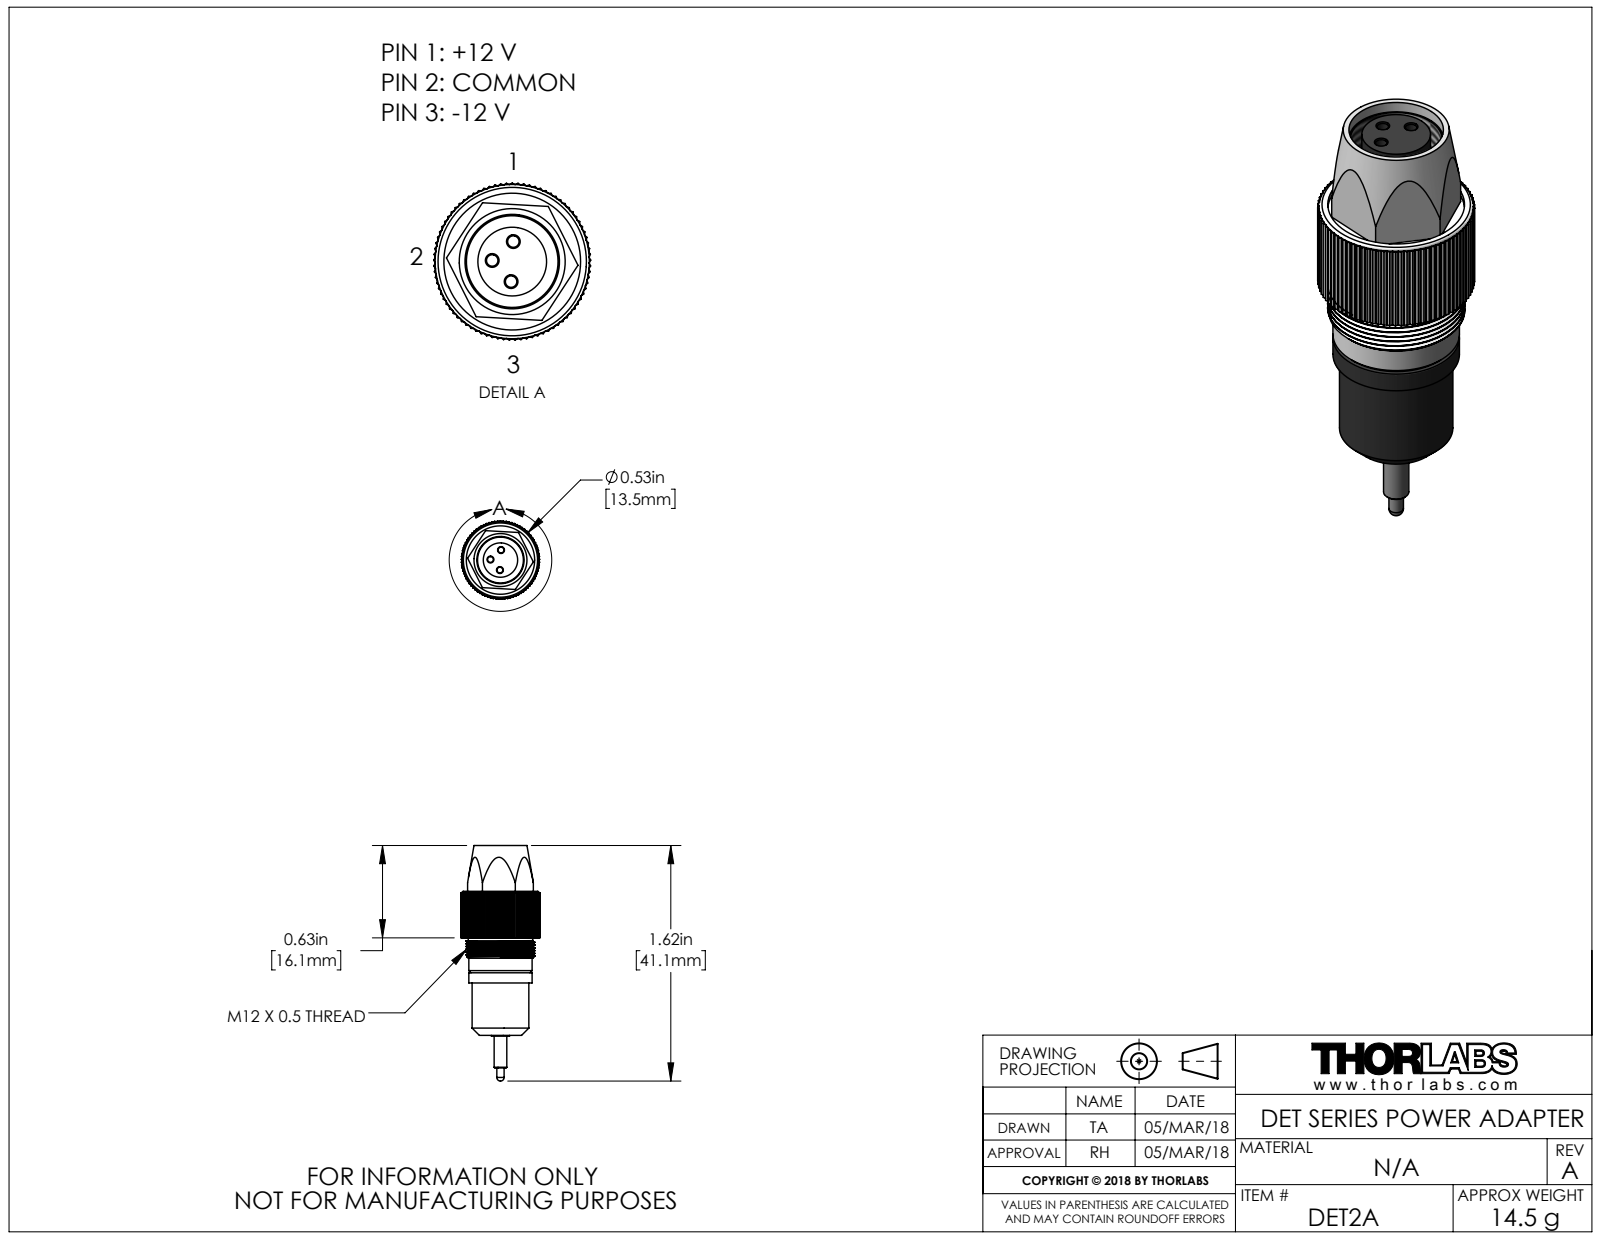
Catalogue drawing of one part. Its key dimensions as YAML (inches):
part_name: "TTN148688-E0W"
step_written_by: "SolidWorks 2016 (AUTOMOTIVE_DESIGN)"
units: inches
bodies: {solids: 5, faces: 448, planar: 307, cylindrical: 117, other: 24}
overall_size: [1.619, 0.54, 0.54]
volume: 0.146
surface_area: 5.638
round_holes:
  - {diameter: 0.039, count: 3}
  - {diameter: 0.067, count: 1}
  - {diameter: 0.1, count: 1}
  - {diameter: 0.14, count: 1}
  - {diameter: 0.236, count: 1}
  - {diameter: 0.268, count: 1}
  - {diameter: 0.31, count: 1}
  - {diameter: 0.325, count: 1}
  - {diameter: 0.375, count: 1}
  - {diameter: 0.47, count: 1}
round_bosses_or_shafts:
  - {diameter: 0.055, count: 3}
  - {diameter: 0.472, count: 1}
  - {diameter: 0.435, count: 1}
  - {diameter: 0.435, count: 1}
  - {diameter: 0.4, count: 1}
  - {diameter: 0.39, count: 1}
  - {diameter: 0.315, count: 1}
  - {diameter: 0.125, count: 1}
partial_cylinders:
  - {radius: 0.005, count: 1}
  - {radius: 0.01, count: 1}
  - {radius: 0.265, count: 1}
face_to_face_distances: [0.393, 0.06, 0.332, 0.315, 0.276, 0.335, 0.09, 0.68, 0.77, 0.3]
hole_center_spacings: [0.069, 0.097, 0.098, 0.138]
